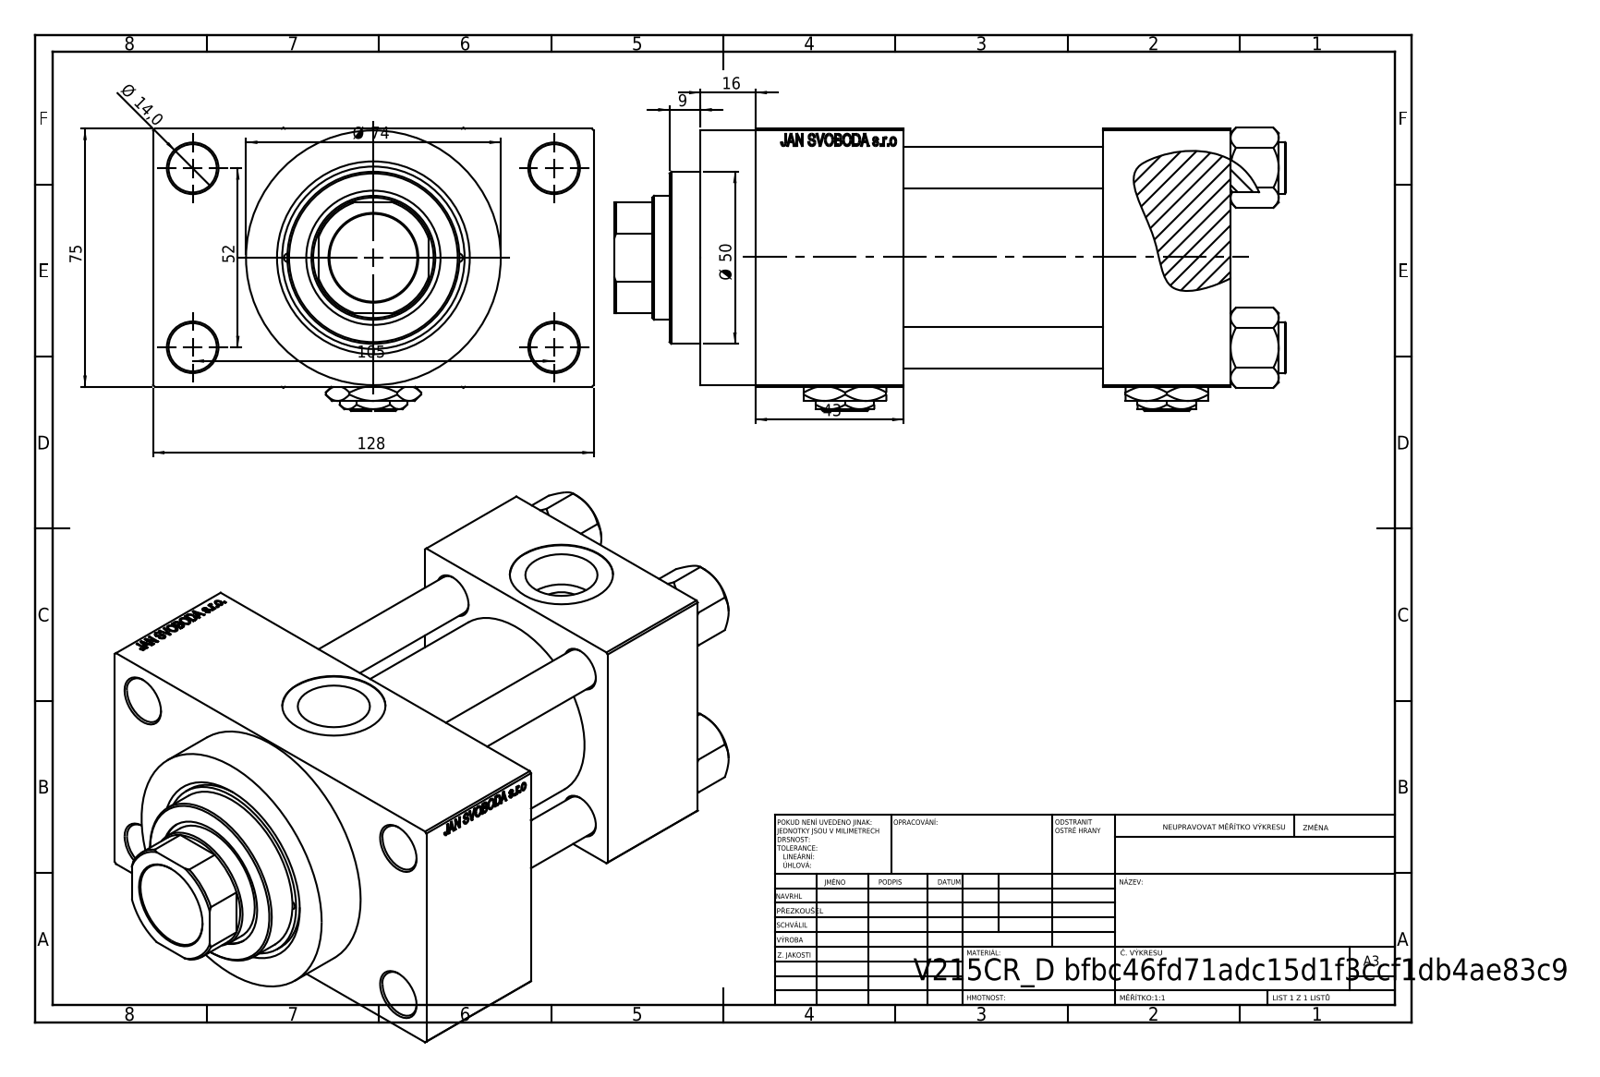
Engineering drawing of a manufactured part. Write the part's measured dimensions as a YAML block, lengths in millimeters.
part_name: "V215CR_VCP_D; V215CR_D_TYCINKA; NUT_M5_D; V215_VC_A (+2 more)"
step_written_by: "SolidWorks 2019 (CONFIG_CONTROL_DESIGN)"
units: millimeters
bodies: {solids: 13, faces: 1215, planar: 549, cylindrical: 104, other: 562}
overall_size: [195, 128, 82.27]
volume: 821732
surface_area: 177975
round_holes:
  - {diameter: 12, count: 4}
  - {diameter: 14, count: 4}
  - {diameter: 2.5, count: 2}
  - {diameter: 7, count: 2}
  - {diameter: 20.96, count: 2}
  - {diameter: 30, count: 2}
  - {diameter: 25.5, count: 1}
  - {diameter: 36, count: 1}
  - {diameter: 39, count: 1}
  - {diameter: 41, count: 1}
  - {diameter: 53, count: 1}
round_bosses_or_shafts:
  - {diameter: 15, count: 4}
  - {diameter: 74, count: 1}
  - {diameter: 56, count: 1}
  - {diameter: 50, count: 1}
partial_cylinders:
  - {radius: 17.5, count: 1}
face_to_face_distances: [75, 58, 37, 95, 101.5, 26.5, 138, 43, 101, 128]
hole_center_spacings: [26.19, 26.35, 36.98, 38.03, 52.3, 57.22, 58.43, 58.59]
